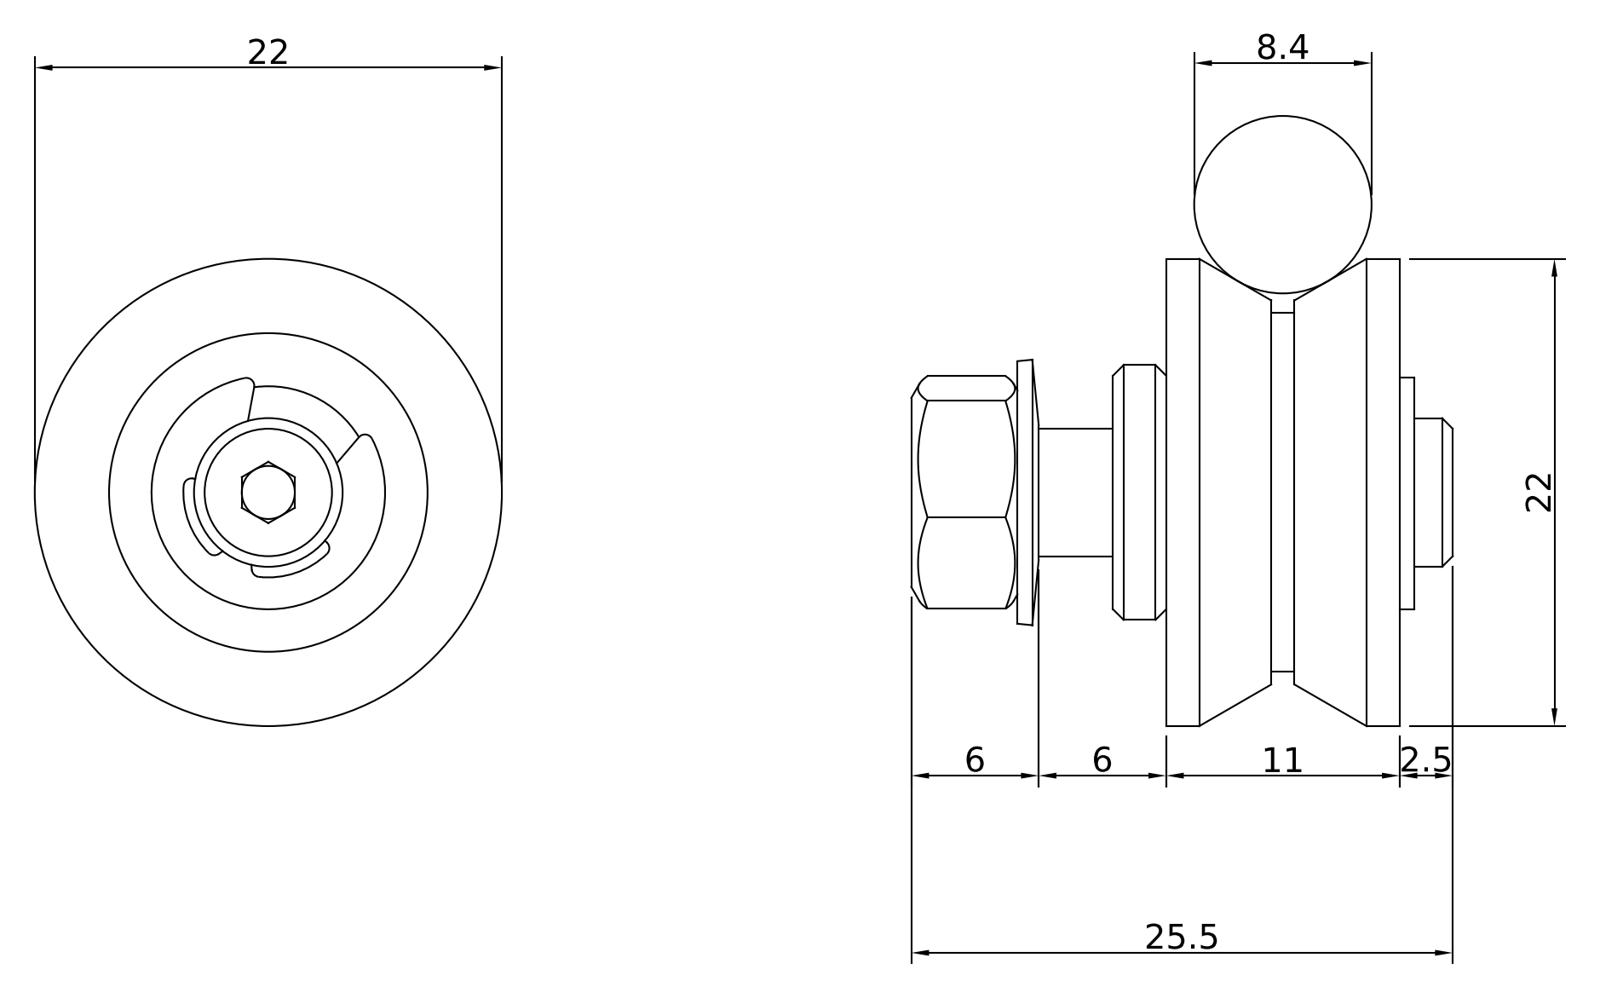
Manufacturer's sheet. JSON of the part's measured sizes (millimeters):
{"part_name": "23.522.00C; 70PE00130-A; 80RT00013R-A; 440000000023 (+2 more)", "step_written_by": "Autodesk Inventor 2022 (AUTOMOTIVE_DESIGN)", "units": "millimeters", "bodies": {"solids": 5, "faces": 102, "planar": 54, "cylindrical": 32, "other": 16}, "overall_size": [25.5, 22, 22], "volume_mm3": 4483, "surface_area_mm2": 3429, "round_holes": [[2.5, 1], [4.92, 1], [5, 1], [15, 1]], "round_bosses_or_shafts": [[22, 1], [16.9, 1], [12, 1], [10, 1], [7, 1], [6, 1]], "partial_cylinders_radius": [[0.38, 11], [4, 1], [5.5, 1]], "face_to_face_distances": [11, 0.5, 10.5, 10, 2.5, 3, 13, 13.5, 11.7, 11.2]}
